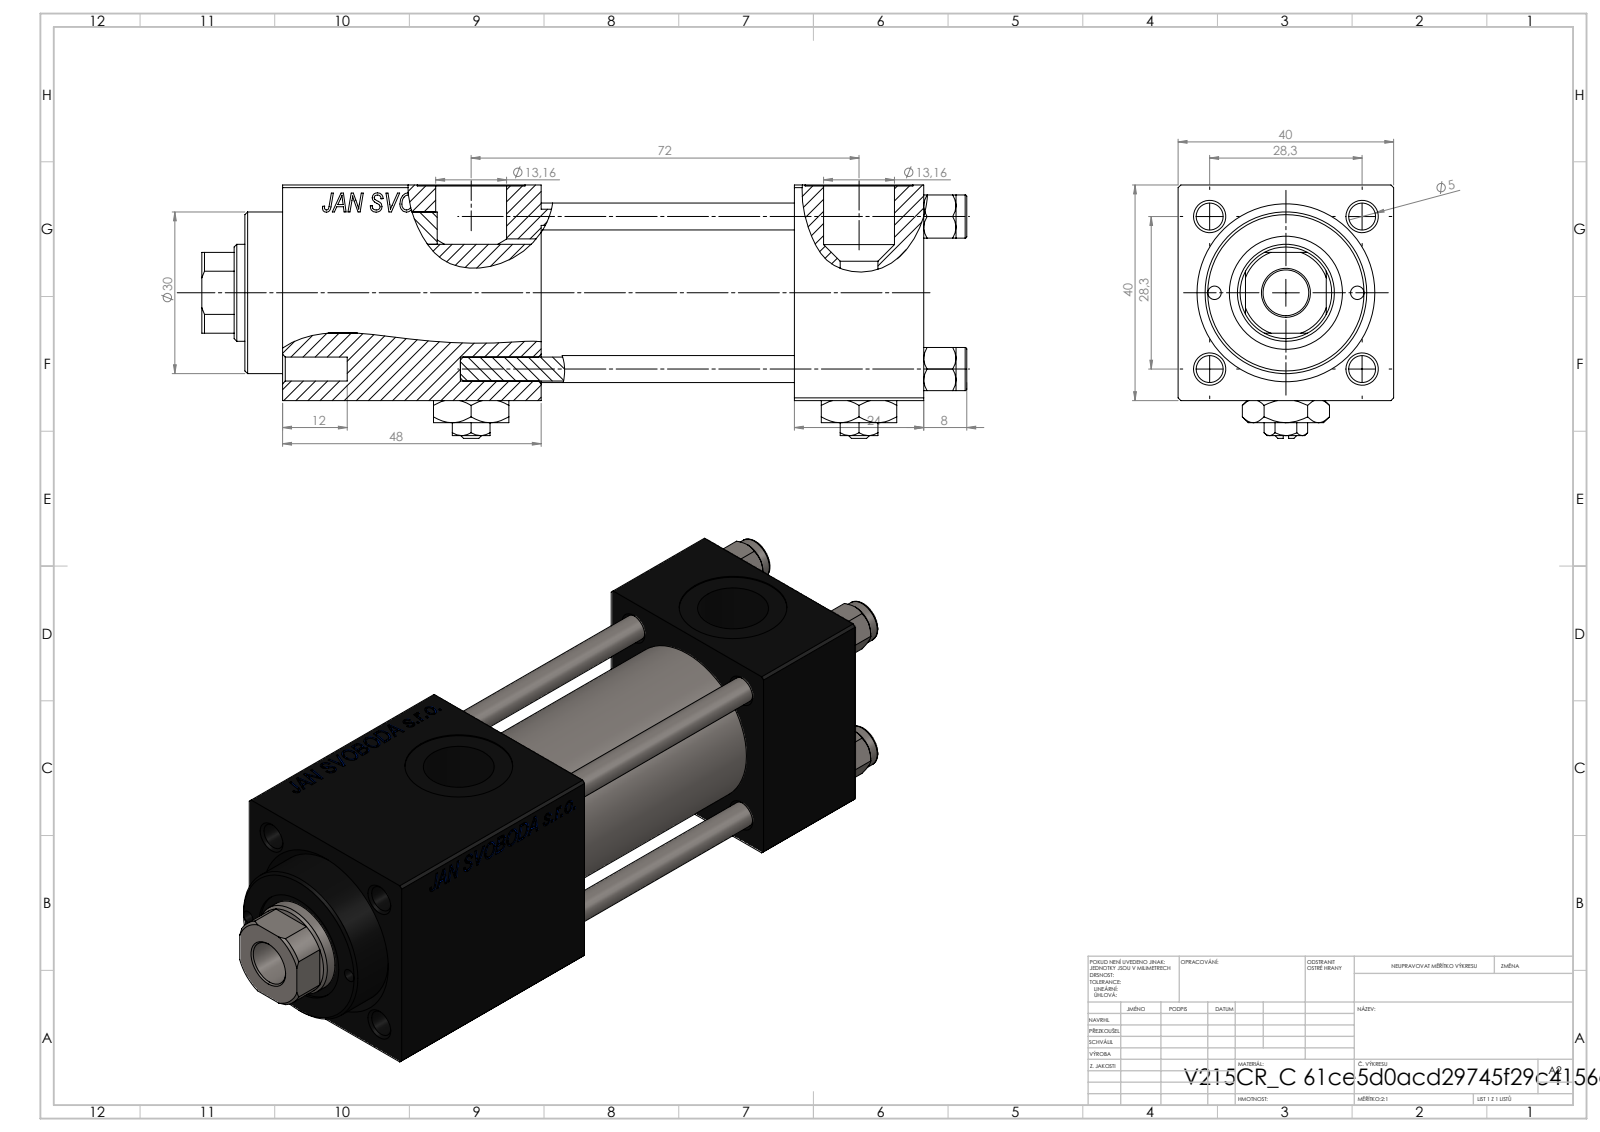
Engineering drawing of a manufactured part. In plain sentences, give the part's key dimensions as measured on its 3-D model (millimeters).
The part is named "V215CR_C_TYCINKA; V215CR_C_Body; V215_VC_A; V215CR_VCP_C (+2 more)". Its 3-D file was written by "SolidWorks 2019 (CONFIG_CONTROL_DESIGN)". It is 13 solids with 1251 faces: 573 planar, 100 cylindrical and 578 other. Overall it measures 142 by 47 by 40 millimeters. Its volume is 148 072 cubic millimeters and its surface area 58 738 square millimeters. Round holes: 4 of diameter 5, 3 of diameter 20, 2 of diameter 2.5, 2 of diameter 7, 2 of diameter 13.16, 1 of diameter 8.5, 1 of diameter 18, 1 of diameter 21, 1 of diameter 25, 1 of diameter 30. Round bosses or shafts: 4 of diameter 8, 1 of diameter 31. Partial cylindrical surfaces (rounded edges, fillets, slot ends): 1 of radius 8.5. The main face-to-face distances are 40, 24, 39.8, 47, 71, 90.3, 66.3, 19.3, 48, 95. The hole center spacings are 14.18, 20.01, 28.3, 30.84, 13.25, 40.02, 26.5, 72.
